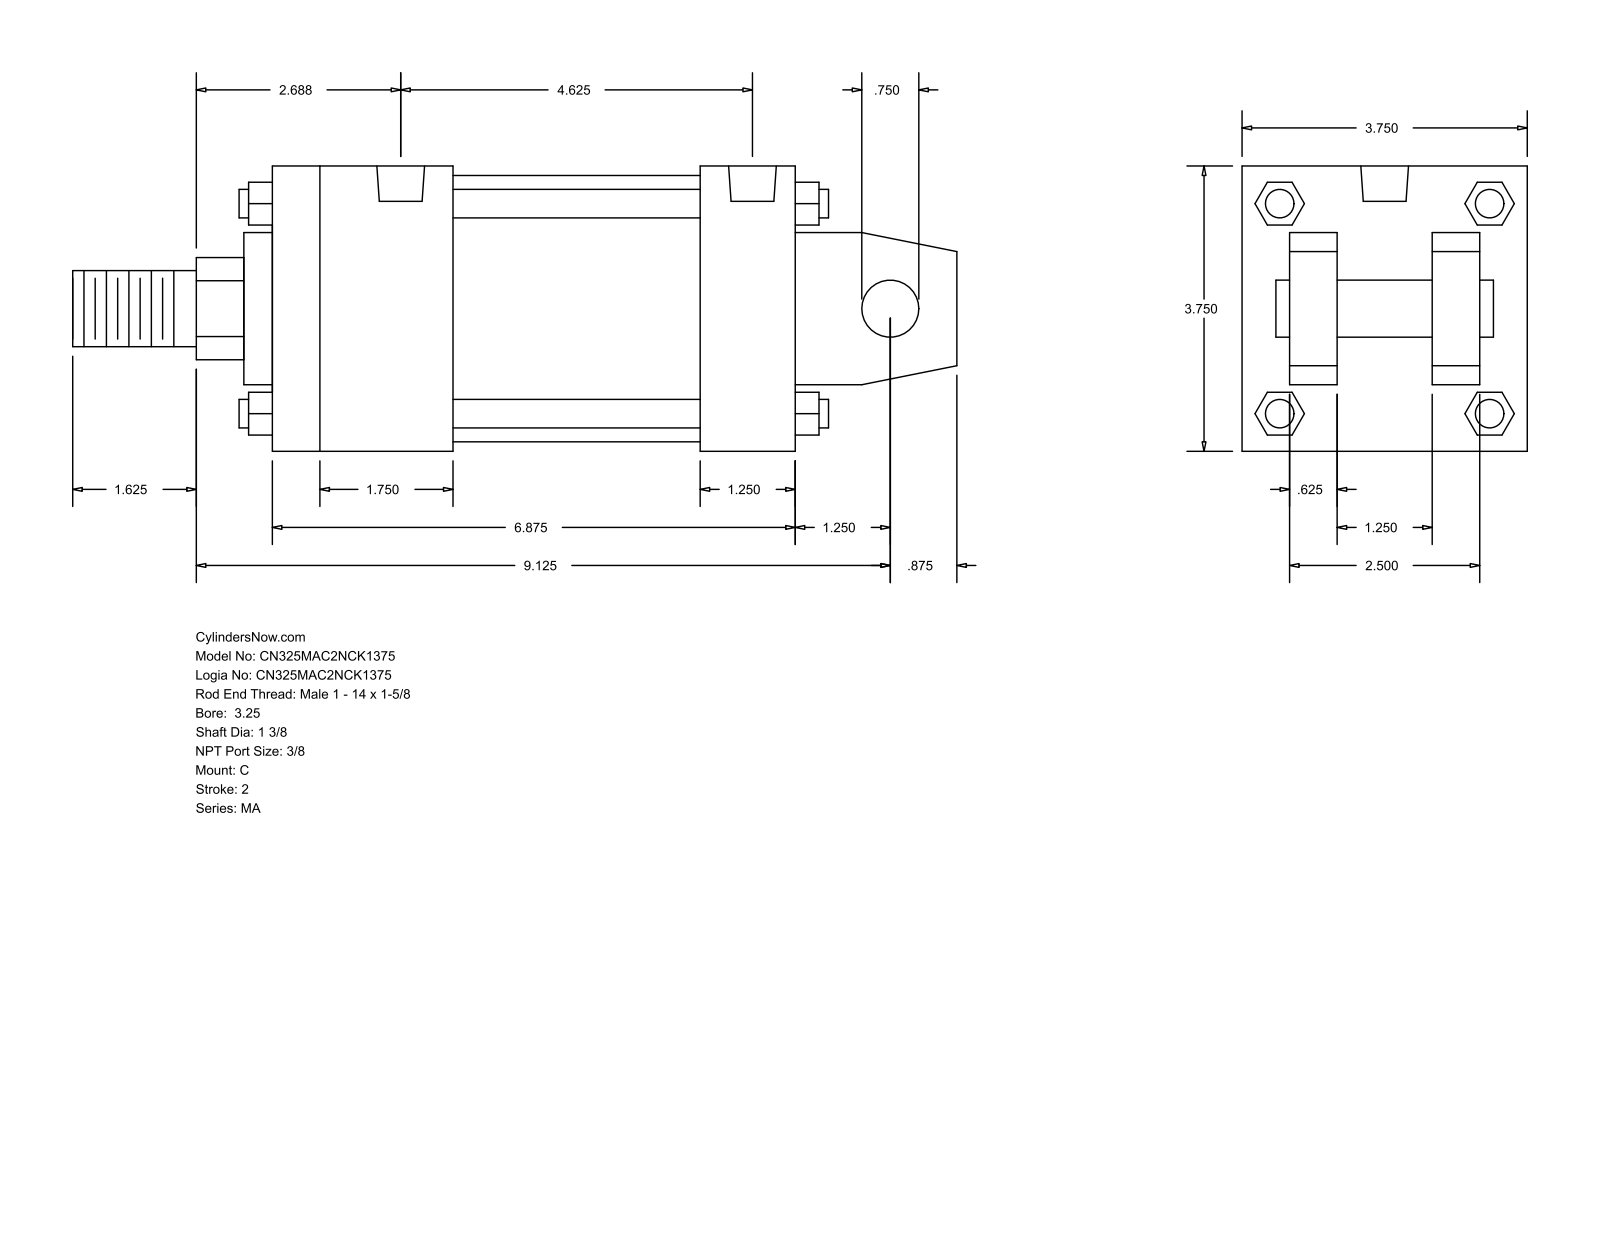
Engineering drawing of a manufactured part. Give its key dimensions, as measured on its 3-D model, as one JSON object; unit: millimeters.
{"part_name": "MA_C__0325_1.375", "step_written_by": "GSSL Pune (CONFIG_CONTROL_DESIGN)", "units": "millimeters", "bodies": {"solids": 0, "faces": 139, "planar": 108, "cylindrical": 31, "other": 0}, "overall_size": [295.27, 95.25, 95.25], "round_holes": [[11.11, 4], [15.93, 2]], "round_bosses_or_shafts": [[9.53, 4], [88.9, 1], [50.8, 1], [34.92, 1], [25.4, 1], [19.05, 1]], "partial_cylinders_radius": [[17.06, 1]], "face_to_face_distances": [95.24, 15.87, 63.5, 174.63, 31.74, 79.37, 47.63, 142.88, 31.75, 60.32], "hole_center_spacings": [4.77, 107.94, 112.71, 117.48]}
